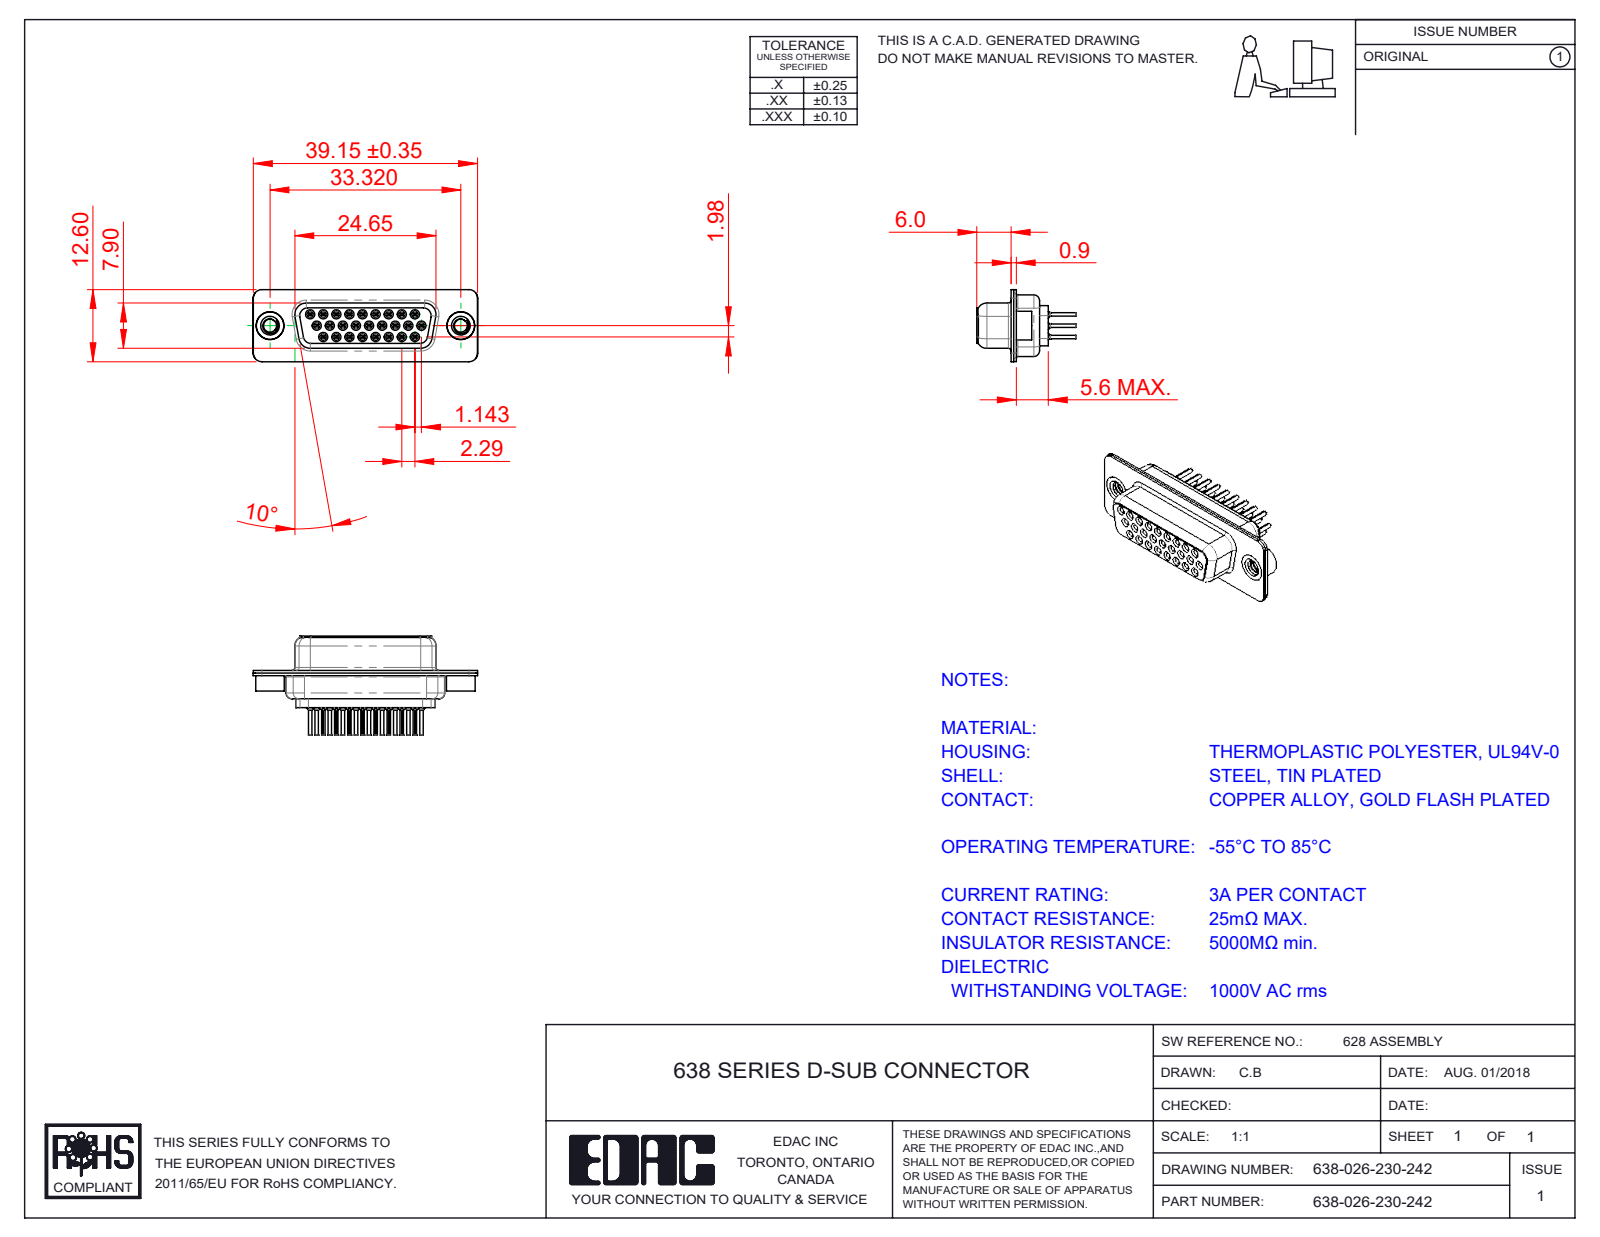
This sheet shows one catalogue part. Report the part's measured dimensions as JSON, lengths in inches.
{"part_name": "638 4-40 Threaded Rivet; 638 Contact Row 1_30; 638 Housing_26 Contacts; 638-026-230-242 (+4 more)", "step_written_by": "SolidWorks 2020 (CONFIG_CONTROL_DESIGN)", "units": "inches", "bodies": {"solids": 31, "faces": 3581, "planar": 873, "cylindrical": 995, "other": 1713}, "overall_size": [1.543, 0.681, 0.496], "volume_in3": 0.135, "surface_area_in2": 12.88, "round_holes": [[0.008, 26], [0.031, 26], [0.039, 26], [0.043, 26], [0.063, 26], [0.067, 26], [0.071, 26], [0.089, 2], [0.157, 2], [0.159, 2], [0.191, 2]], "round_bosses_or_shafts": [[0.079, 26], [0.059, 26], [0.047, 26], [0.024, 26], [0.197, 2], [0.195, 2], [0.189, 2]], "partial_cylinders_radius": [[0.004, 52], [0.059, 20], [0.011, 18], [0.079, 12], [0.061, 8], [0.053, 5], [0.01, 4], [0.02, 4]], "face_to_face_distances": [0.018, 0.016, 0.056, 0.35, 0.035, 0.26, 0.09, 0.055, 0.033, 0.278], "hole_center_spacings": [0.156, 0.09, 0.18, 0.238, 0.09, 0.324, 0.27, 0.413]}
